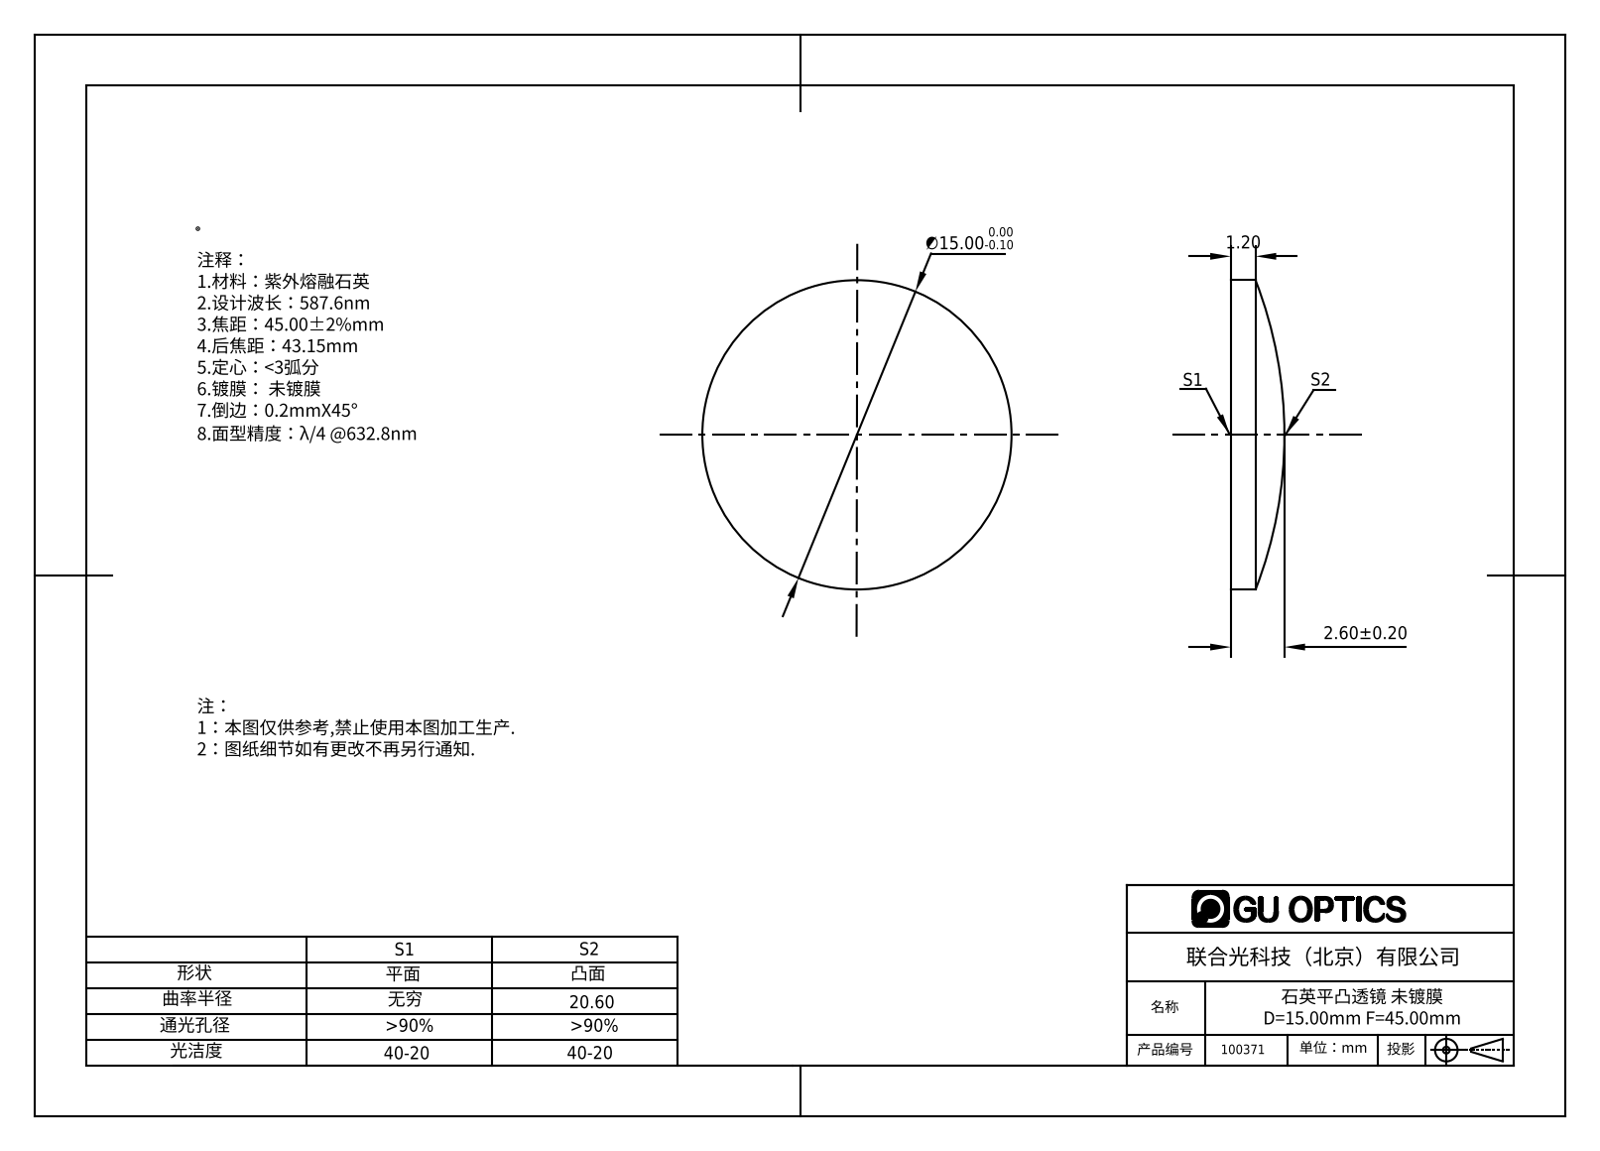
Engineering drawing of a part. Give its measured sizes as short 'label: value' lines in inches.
name: 100371
written by: SolidWorks 2016 (AUTOMOTIVE_DESIGN)
unit: in
bodies: 1 solid, 5 faces (1 planar, 2 cylindrical, 2 other)
size: 0.591 × 0.591 × 0.102
volume: 0.021 in³; area: 0.645 in²
bosses: 1× ⌀0.591
